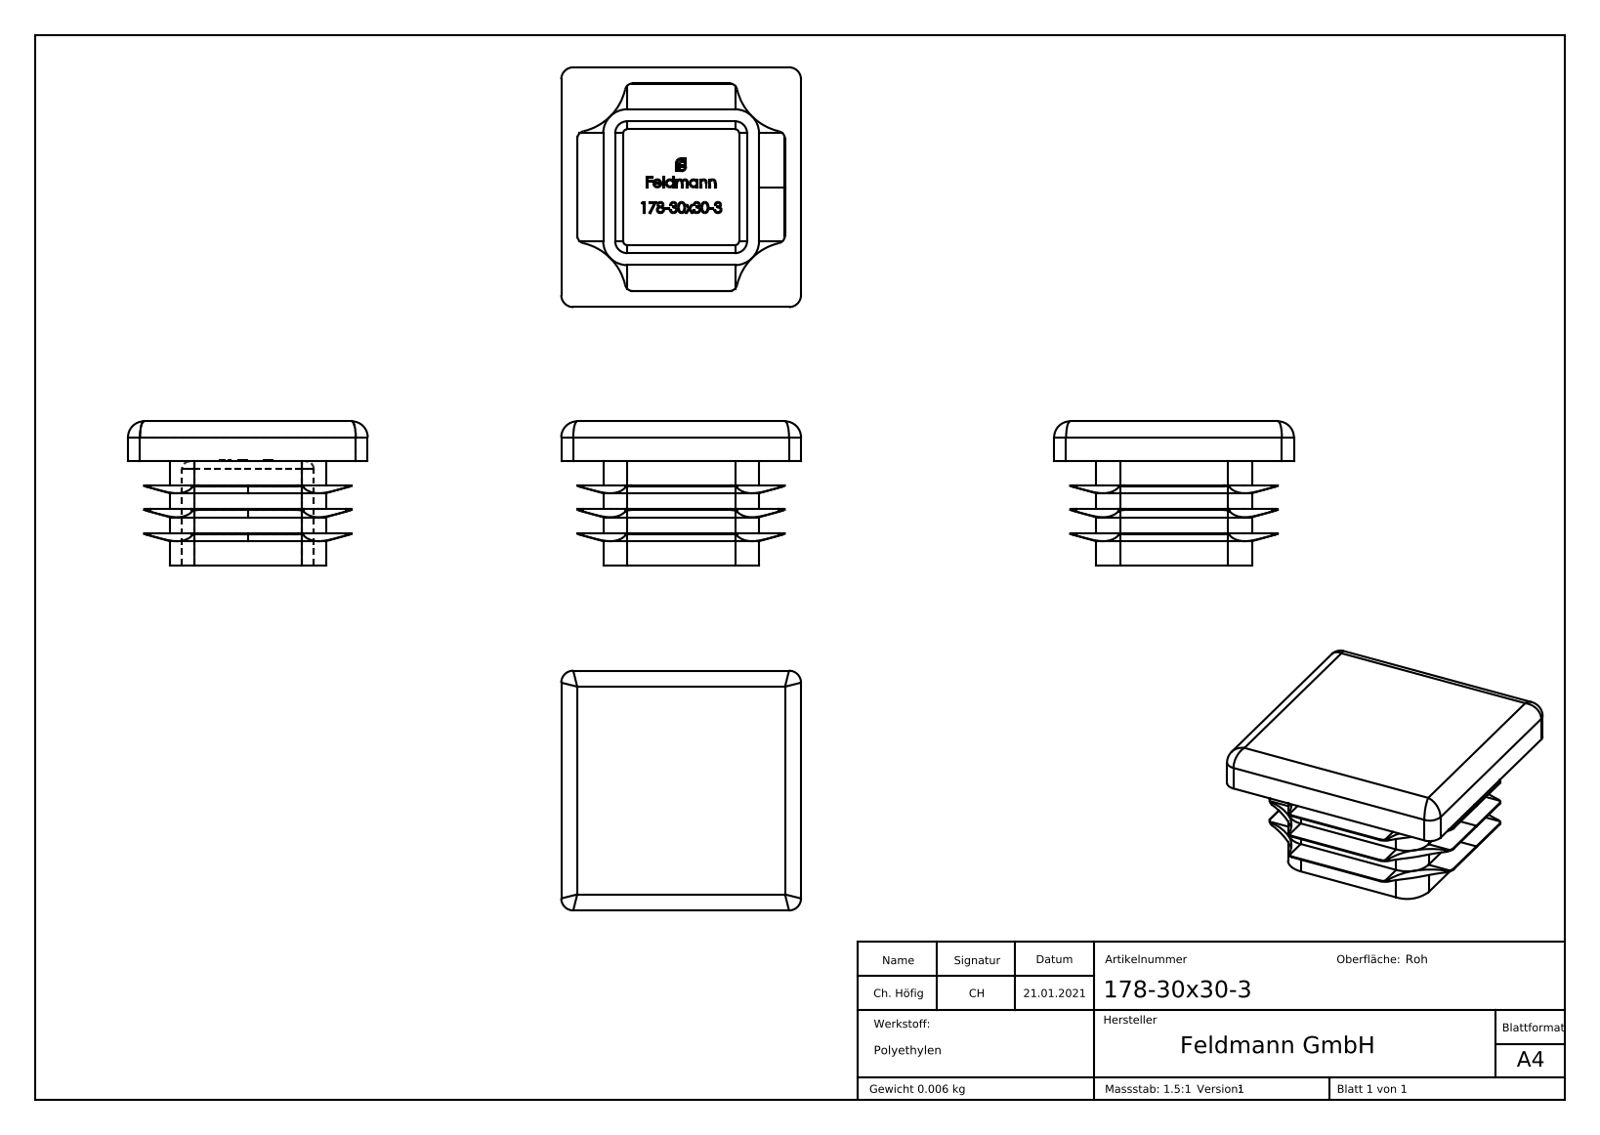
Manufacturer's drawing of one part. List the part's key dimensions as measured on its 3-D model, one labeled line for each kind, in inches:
Part name (STEP PRODUCT): 178-30x30-3
STEP written by: SolidWorks 2018 (CONFIG_CONTROL_DESIGN)
Units: inches
Bodies: 1 solid, 465 faces (235 planar, 83 cylindrical, 147 other)
Overall size (bounding box): 1.181 × 1.181 × 0.709
Volume: 0.37 in³ · Surface area: 7.86 in²
Partial cylindrical surfaces — rounded edges, fillets, slot ends (radius × count): R0.039 ×12, R0.059 ×8, R0.079 ×4, R0.118 ×4, R0.276 ×4
Main face-to-face distances: 0.197, 0.709, 0.118, 0.059, 0.236, 0.114, 0.207, 0.266, 0.915, 0.974
